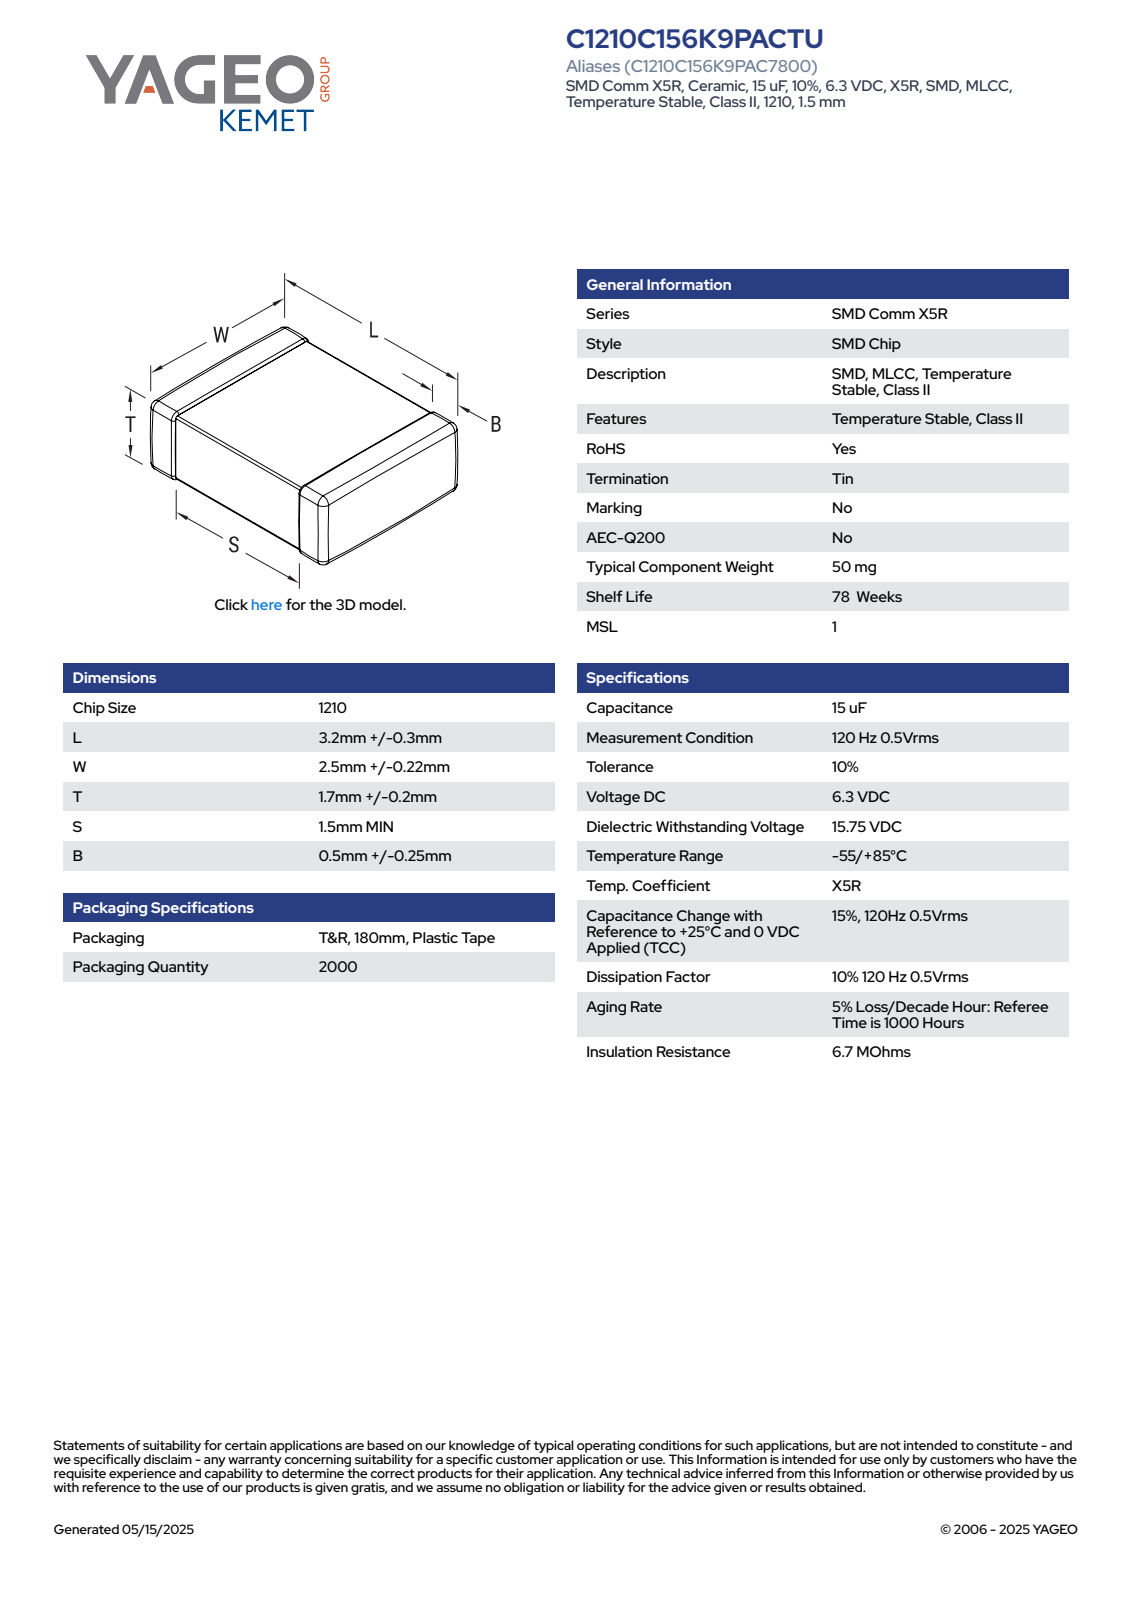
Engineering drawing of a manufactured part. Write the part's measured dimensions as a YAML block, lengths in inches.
part_name: "CCS_CCSTD_1210_L3.5W2.72T1.9B0.5"
step_written_by: "SolidWorks 2021 (AUTOMOTIVE_DESIGN)"
units: inches
bodies: {solids: 4, faces: 125, planar: 71, cylindrical: 38, other: 16}
overall_size: [0.138, 0.107, 0.075]
volume: 0.001
surface_area: 0.067
face_to_face_distances: [0.072, 0.07, 0.138, 0.105, 0.102, 0.075, 0.107, 0.07, 0.073, 0.059]
